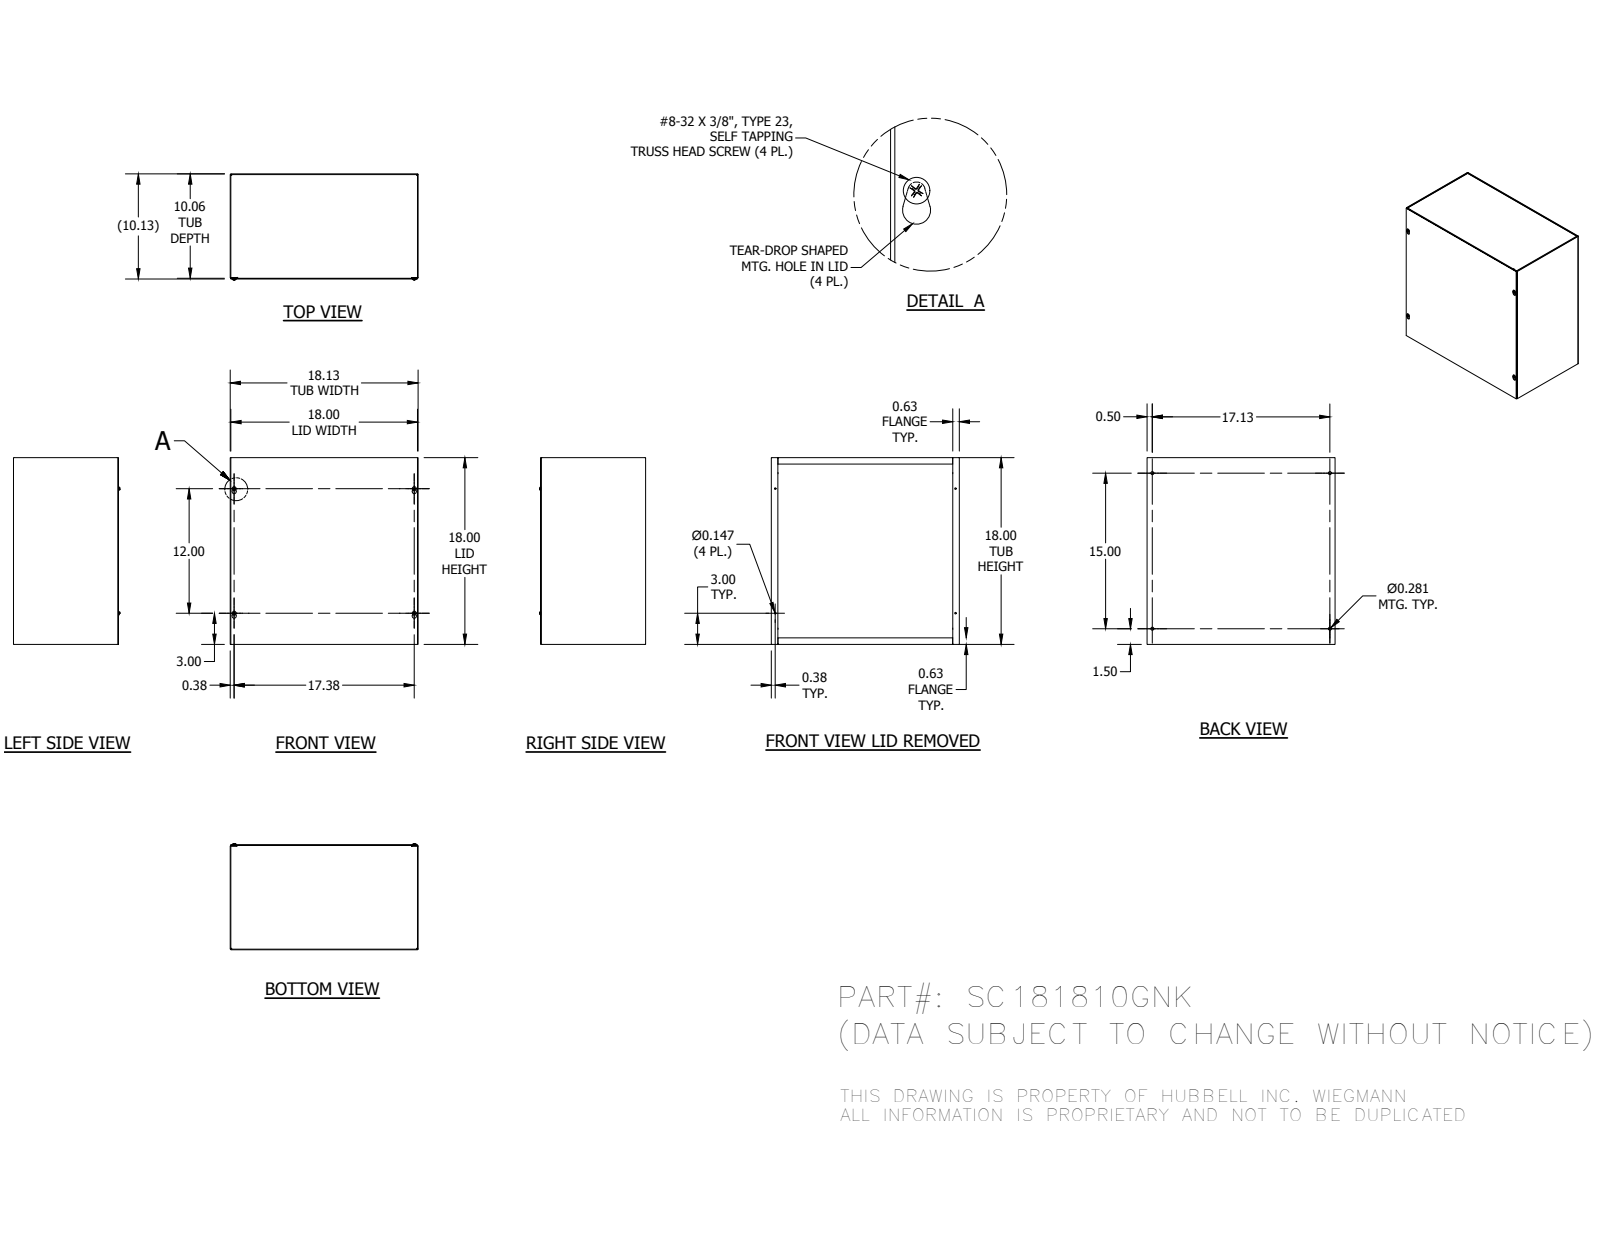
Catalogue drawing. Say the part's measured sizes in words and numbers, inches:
The part is named "SC181810GNKBLR; SC1810GNKTB; SC1818GLPA; 34056 (+1 more)". Its 3-D file was written by "Autodesk Inventor 2014 (AUTOMOTIVE_DESIGN)". It is 8 solids with 268 faces: 152 planar, 48 cylindrical and 68 other. Overall it measures 18.125 by 18 by 10.225 inches. Its volume is 90.5 cubic inches and its surface area 2 916 square inches. Round holes: 4 of diameter 0.147, 4 of diameter 0.281. Round bosses or shafts: 4 of diameter 0.384, 4 of diameter 0.164. Partial cylindrical surfaces (rounded edges, fillets, slot ends): 12 of radius 0.016, 12 of radius 0.078, 4 of radius 0.125, 4 of radius 0.203. The main face-to-face distances are 0.063, 18, 10, 17.937, 18.063, 10.063, 10.062, 0.062, 10.125, 17.875. The hole center spacings are 1.505, 13.5, 17.315, 21.905, 12, 15, 17.125, 17.375.
